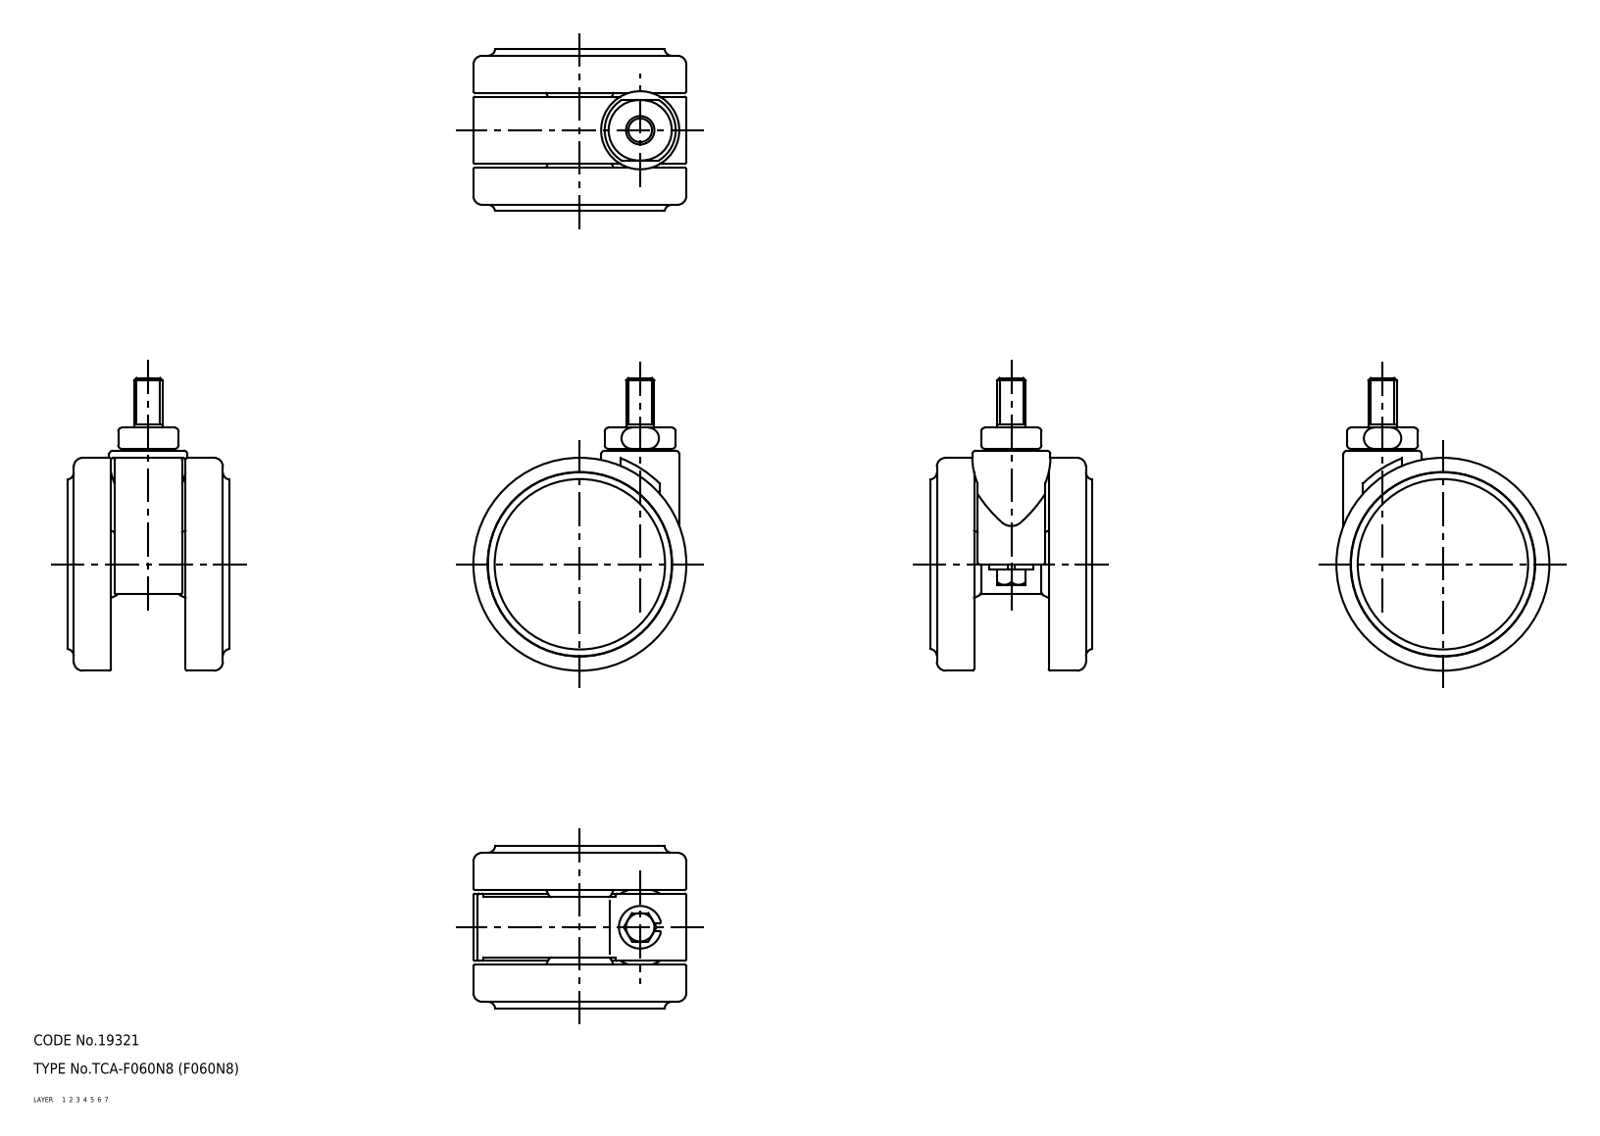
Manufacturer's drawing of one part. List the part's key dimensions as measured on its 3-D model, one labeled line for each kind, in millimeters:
Part name (STEP PRODUCT): 67118946; 67118959; 67118972; 67118985
STEP written by: CADfix (AUTOMOTIVE_DESIGN)
Units: millimetres
Bodies: 4 solids, 150 faces (0 planar, 0 cylindrical, 150 other)
Overall size (bounding box): 82.5 × 60 × 45.6
Volume: 85 912 mm³ · Surface area: 27 364 mm²
